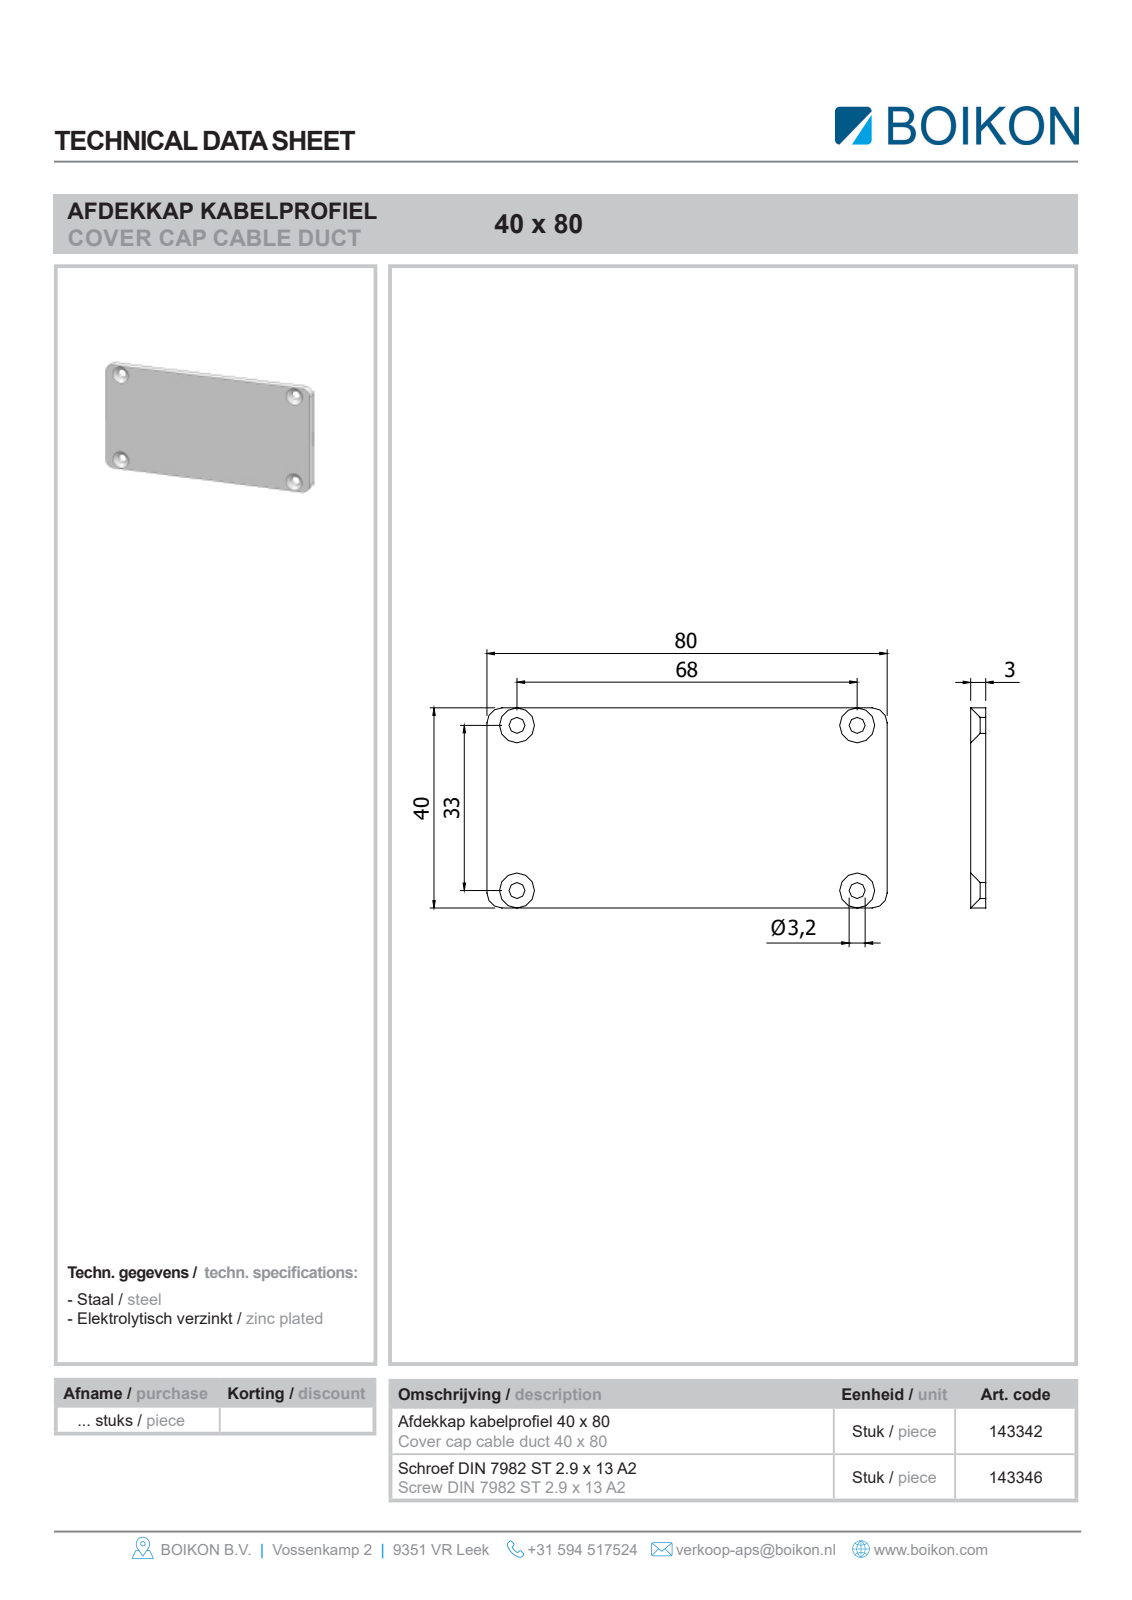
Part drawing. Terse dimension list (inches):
name: Root; 143342Afdekkap kabelprofiel 40x80BOIKON0; 143346Schroef DIN7982 ST 2.9 x 13 A2Tapping screws0
written by: HiCAD 2013 1802.4 Build 509 (AUTOMOTIVE_DESIGN)
unit: in
bodies: 5 solids, 110 faces (42 planar, 16 cylindrical, 52 other)
size: 3.15 × 1.575 × 0.511
volume: 0.59 in³; area: 11.87 in²
holes: 4× ⌀0.134
bosses: 4× ⌀0.217, 4× ⌀0.086
rounds: 4× R0.118
face distances: 0.118, 1.575, 3.15, 0.022, 0.127, 0.149, 1.426, 1.448, 1.299, 0.225
hole spacings: 1.299, 2.677, 2.976
